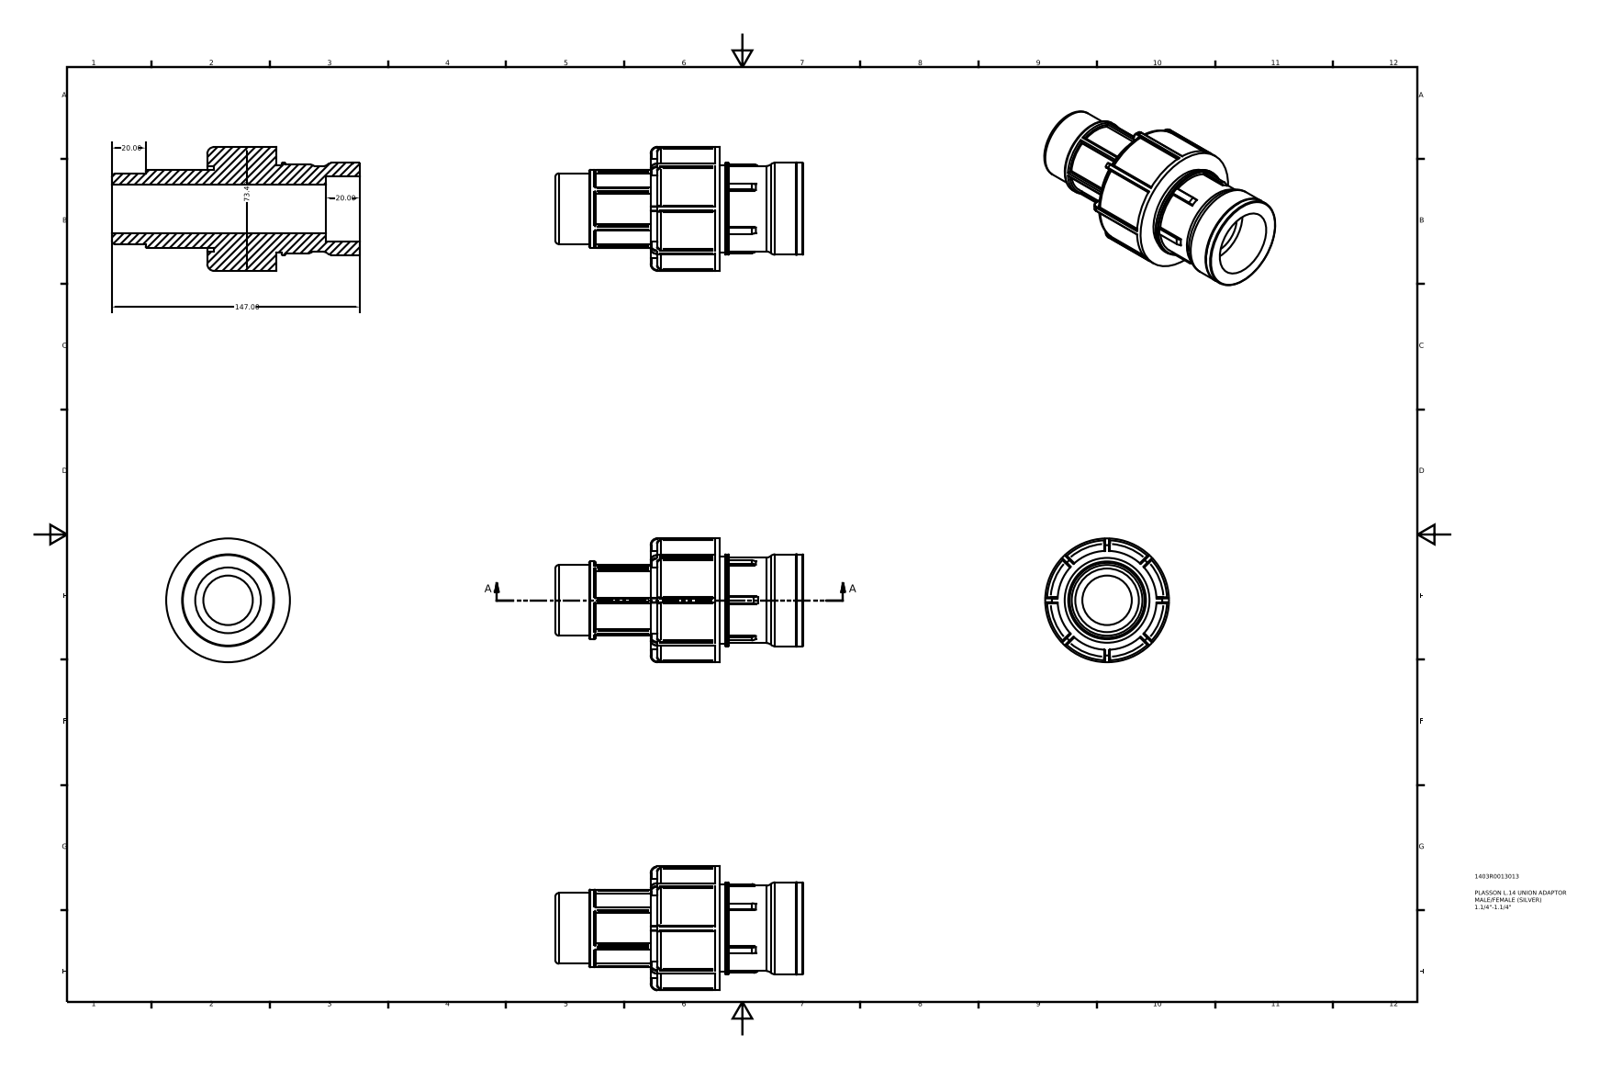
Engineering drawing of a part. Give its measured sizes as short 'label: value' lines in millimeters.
name: 1403R0013013
written by: Autodesk Inventor 2015 (AUTOMOTIVE_DESIGN)
unit: mm
bodies: 1 solid, 267 faces (77 planar, 126 cylindrical, 64 other)
size: 147 × 73.4 × 73.4
volume: 235 920 mm³; area: 49 734 mm²
holes: 1× ⌀29.34, 1× ⌀38.95, 1× ⌀50.29
bosses: 1× ⌀73.4, 1× ⌀71.2, 1× ⌀58.67, 1× ⌀54.53, 1× ⌀51.81, 1× ⌀50.64, 1× ⌀46.1, 1× ⌀41.91
rounds: 58× R0.37, 12× R0.39, 12× R0.84, 5× R3.67
face distances: 37.17, 86.41, 49.24, 4, 41.17, 90.41, 20, 127, 70.41, 66.41
